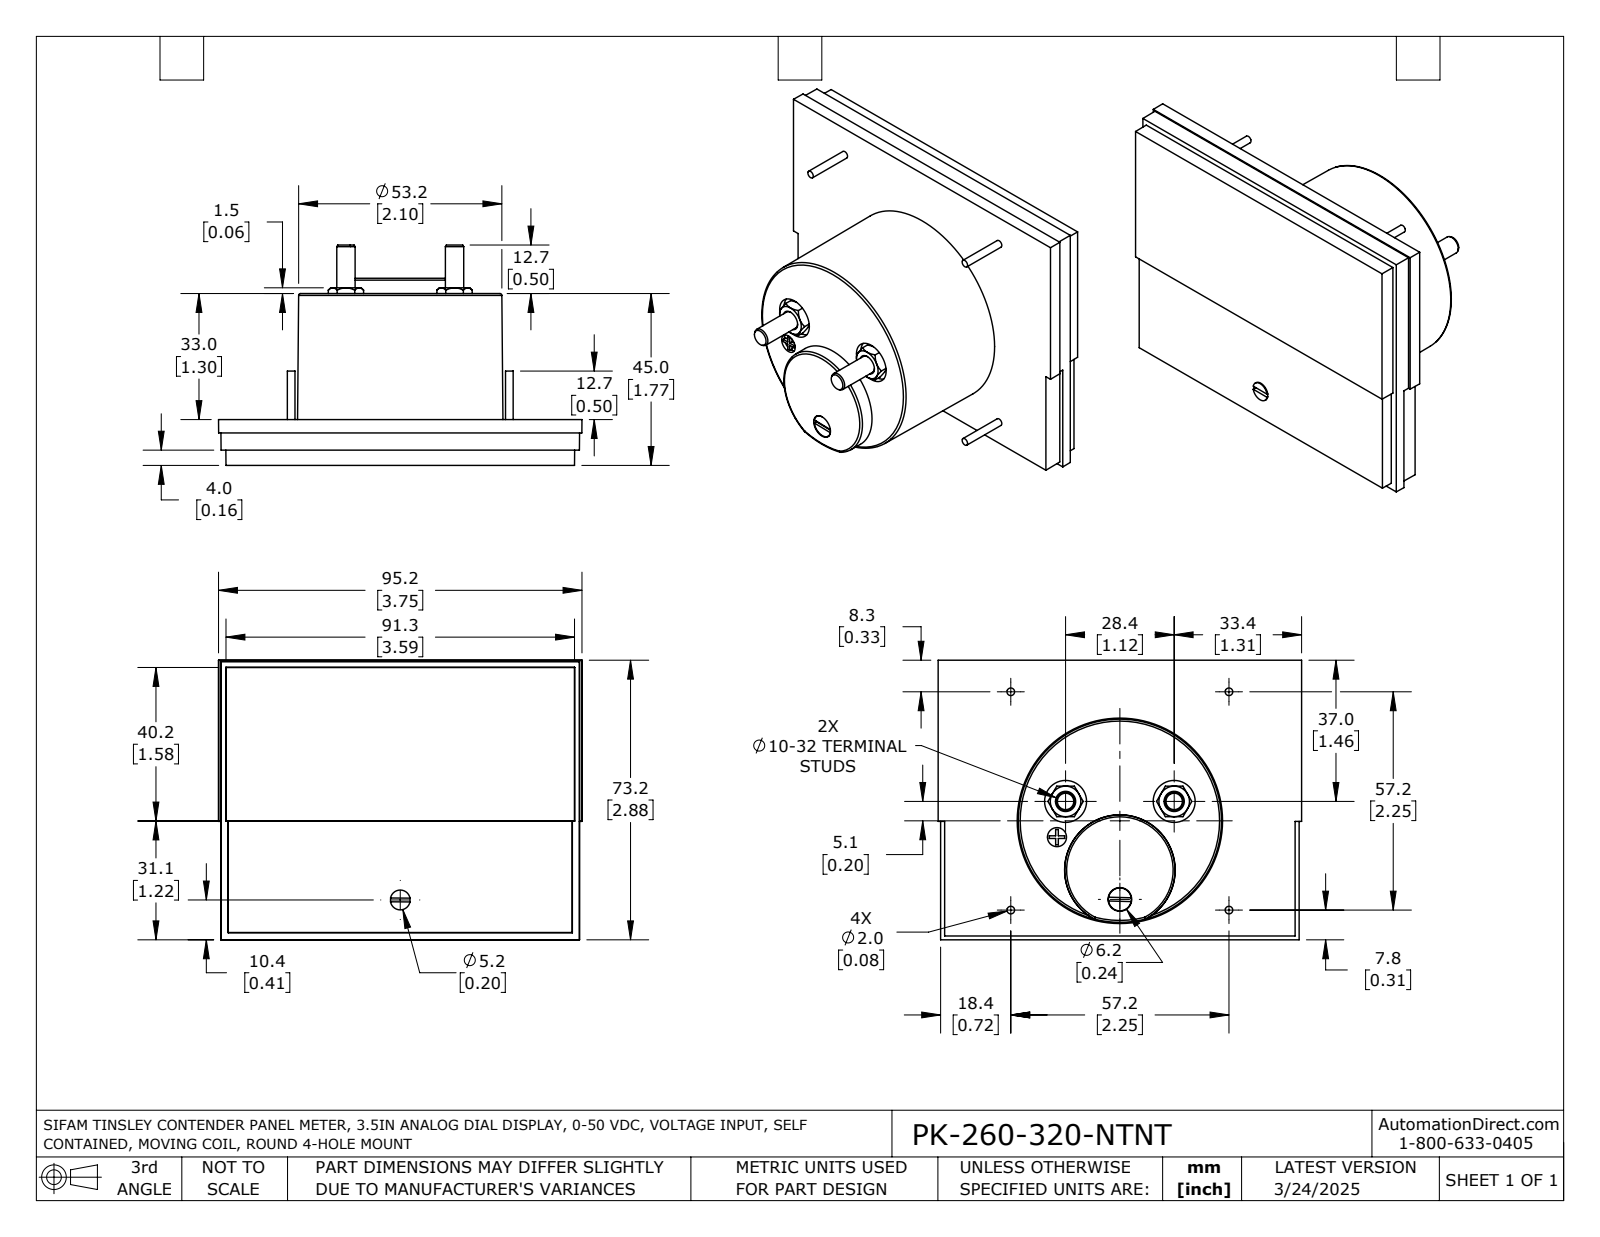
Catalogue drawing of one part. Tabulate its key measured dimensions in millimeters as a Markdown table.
| quantity | value |
| --- | --- |
| part name | PK-260-320-NTNT |
| STEP written by | SolidWorks 2021 (AUTOMOTIVE_DESIGN) |
| units | millimeters |
| bodies | 1 solid, 163 faces (76 planar, 31 cylindrical, 56 other) |
| overall size | 95.2 × 73.2 × 57.7 |
| volume | 154 800 mm³ |
| surface area | 24 770 mm² |
| round holes (diameter × count) | 11 × 2, 5 × 1, 6.2 × 1 |
| round bosses / shafts (diameter × count) | 2 × 4, 4.8 × 2, 6 × 1, 5.2 × 1 |
| partial cylindrical surfaces (radius × count) | 2.5 × 1 |
| main face-to-face distances | 12, 0.8, 11.3, 45, 33, 44.2, 4, 1.9, 8, 37 |
| hole center spacings | 29.3, 9.6, 23.2, 28.4, 32.1 |
